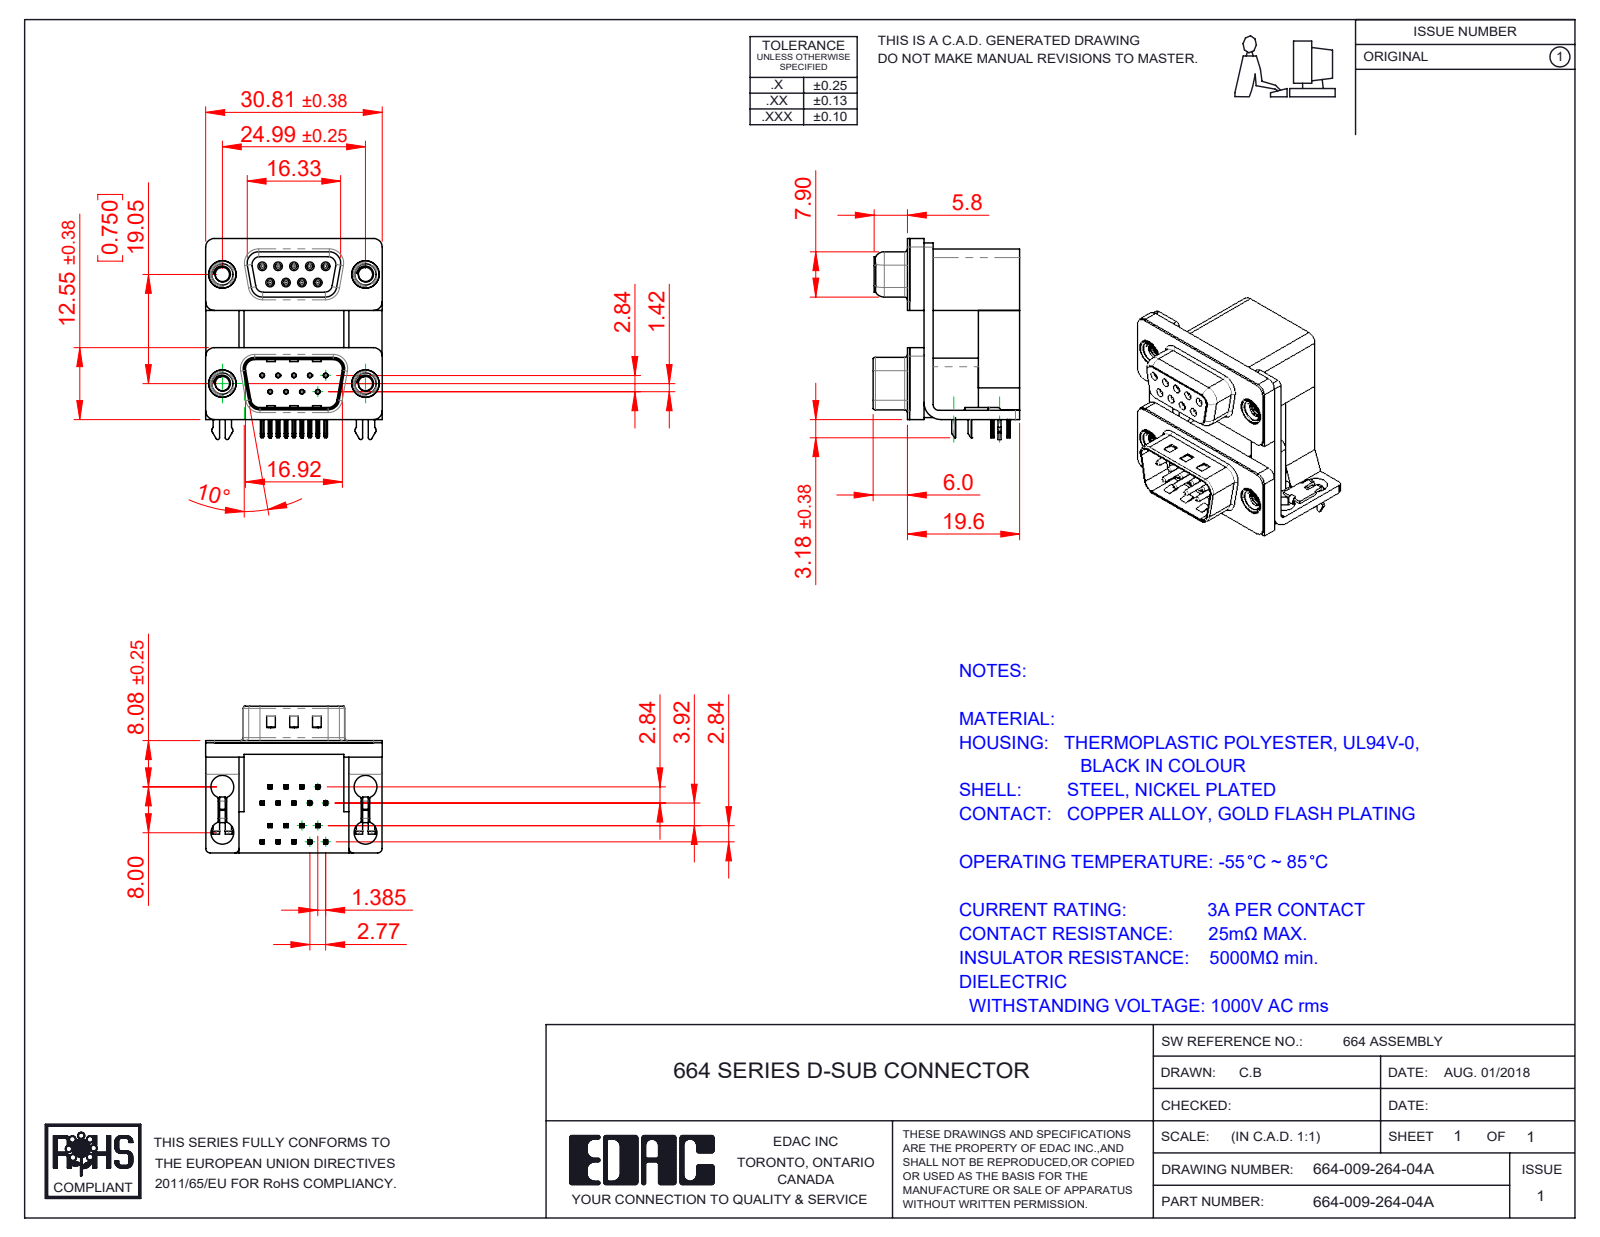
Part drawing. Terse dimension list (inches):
name: 664 Mounting Bracket_2ProngM; 664 Contact Top Lower; 664 Threaded Rivet_M3; 664 Contact Bottom Lower (+8 more)
written by: SolidWorks 2020 (CONFIG_CONTROL_DESIGN)
unit: in
bodies: 31 solids, 2641 faces (1341 planar, 733 cylindrical, 567 other)
size: 1.382 × 1.213 × 1.008
volume: 0.656 in³; area: 19.71 in²
holes: 18× ⌀0.031, 9× ⌀0.014, 9× ⌀0.035, 8× ⌀0.157, 4× ⌀0.098, 4× ⌀0.138, 4× ⌀0.189, 4× ⌀0.197
bosses: 9× ⌀0.047, 9× ⌀0.03, 4× ⌀0.193, 4× ⌀0.187, 4× ⌀0.154
rounds: 73× R0.004, 42× R0.01, 36× R0.006, 18× R0.005, 18× R0.014, 16× R0.02, 13× R0.059, 10× R0.03
face distances: 0.016, 0.098, 0.657, 0.756, 0.283, 0.374, 0.472, 0.063, 0.772, 0.488
hole spacings: 0.124, 0.109, 0.758, 0.75, 0.218, 0.781, 0.641, 0.863
